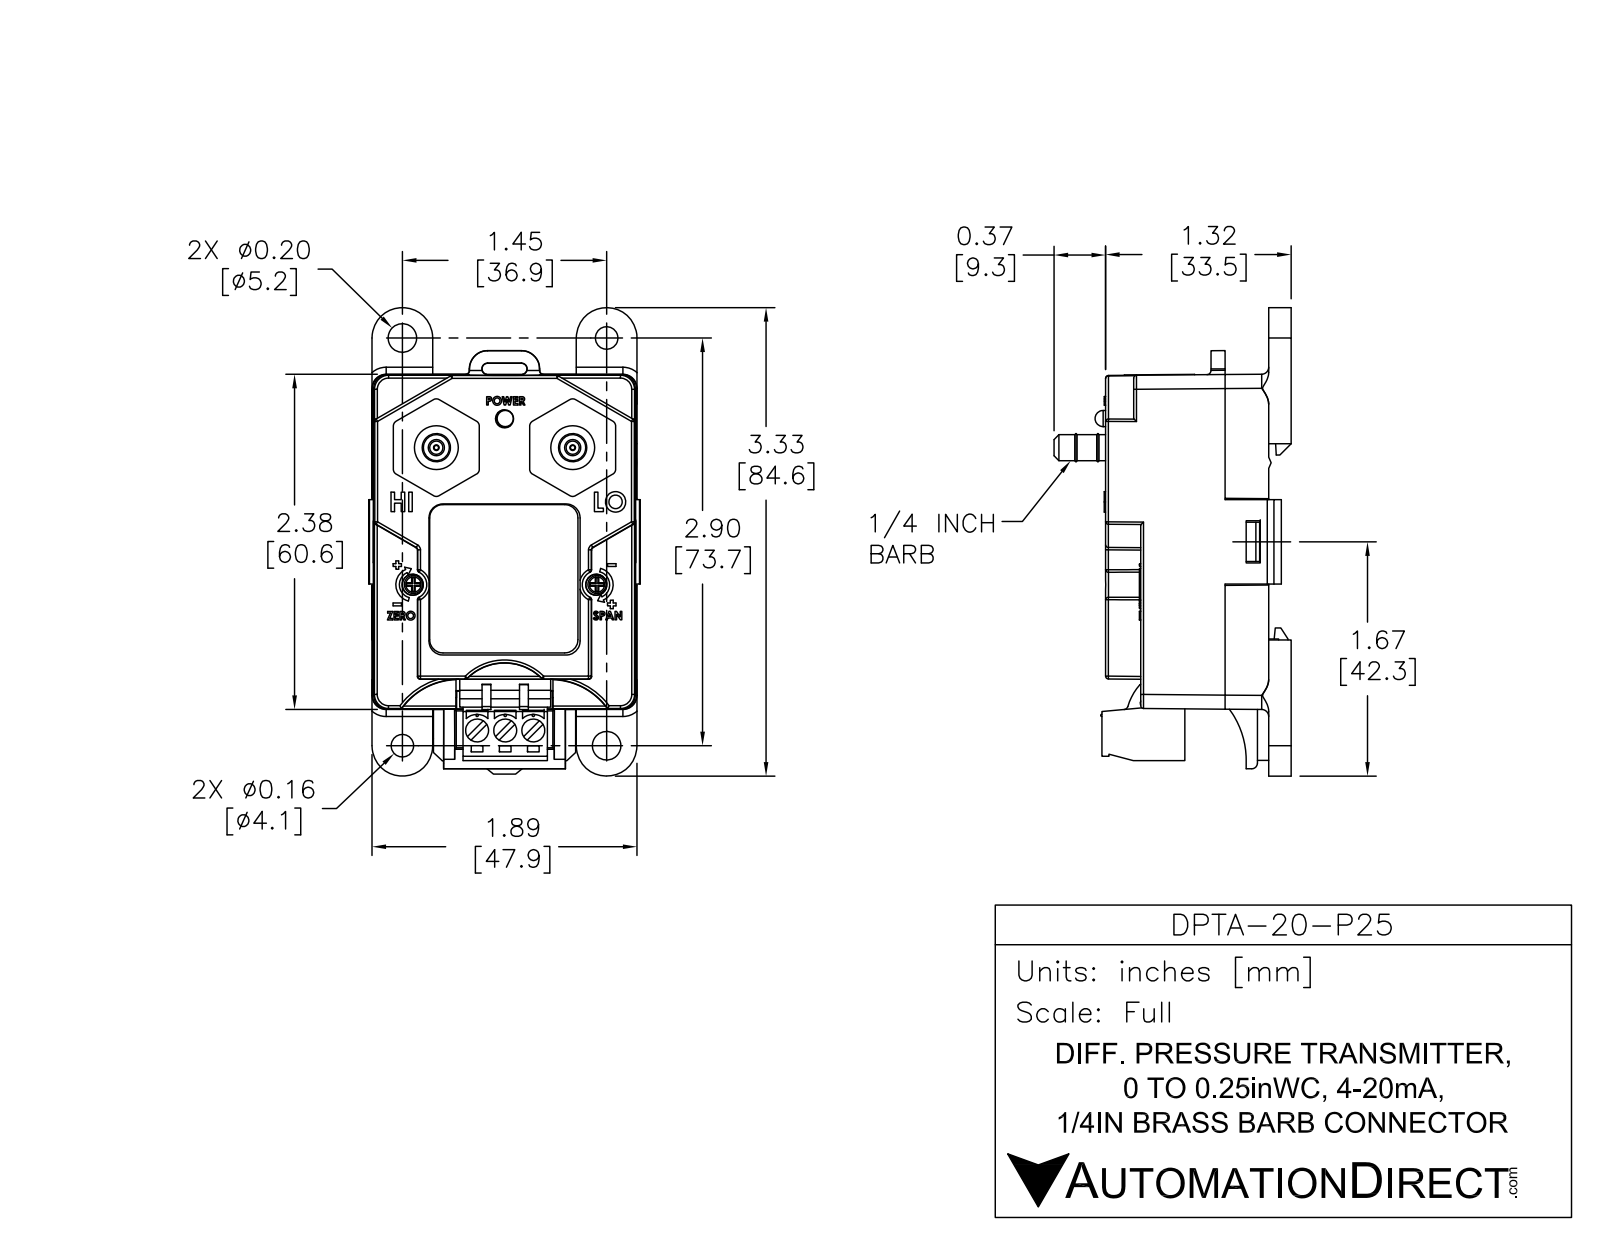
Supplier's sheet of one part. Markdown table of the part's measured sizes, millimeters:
| quantity | value |
| --- | --- |
| part name | DPTA-20-P25 |
| STEP written by | SolidWorks 2011 (AUTOMOTIVE_DESIGN) |
| units | millimeters |
| bodies | 11 solids, 448 faces (354 planar, 85 cylindrical, 9 other) |
| overall size | 85.01 × 49.76 × 43.1 |
| volume | 29 684 mm³ |
| surface area | 34 743 mm² |
| round holes (diameter × count) | 4 × 7, 2.5 × 2, 5.12 × 2, 3.1 × 1 |
| round bosses / shafts (diameter × count) | 5 × 3, 3.5 × 3, 3.5 × 3, 8 × 2, 4.75 × 2, 3 × 1 |
| partial cylindrical surfaces (radius × count) | 3 × 12, 2 × 4, 5.5 × 4, 0.99 × 2, 1.06 × 2, 1.12 × 2, 2.38 × 2, 3.25 × 2 |
| main face-to-face distances | 1, 1.9, 4, 29.1, 0.5, 46.9, 5.9, 5, 33.1, 27.2 |
| hole center spacings | 13.55, 20.73, 23.37, 24.92, 29.43, 34.46, 36.67, 38.22 |
